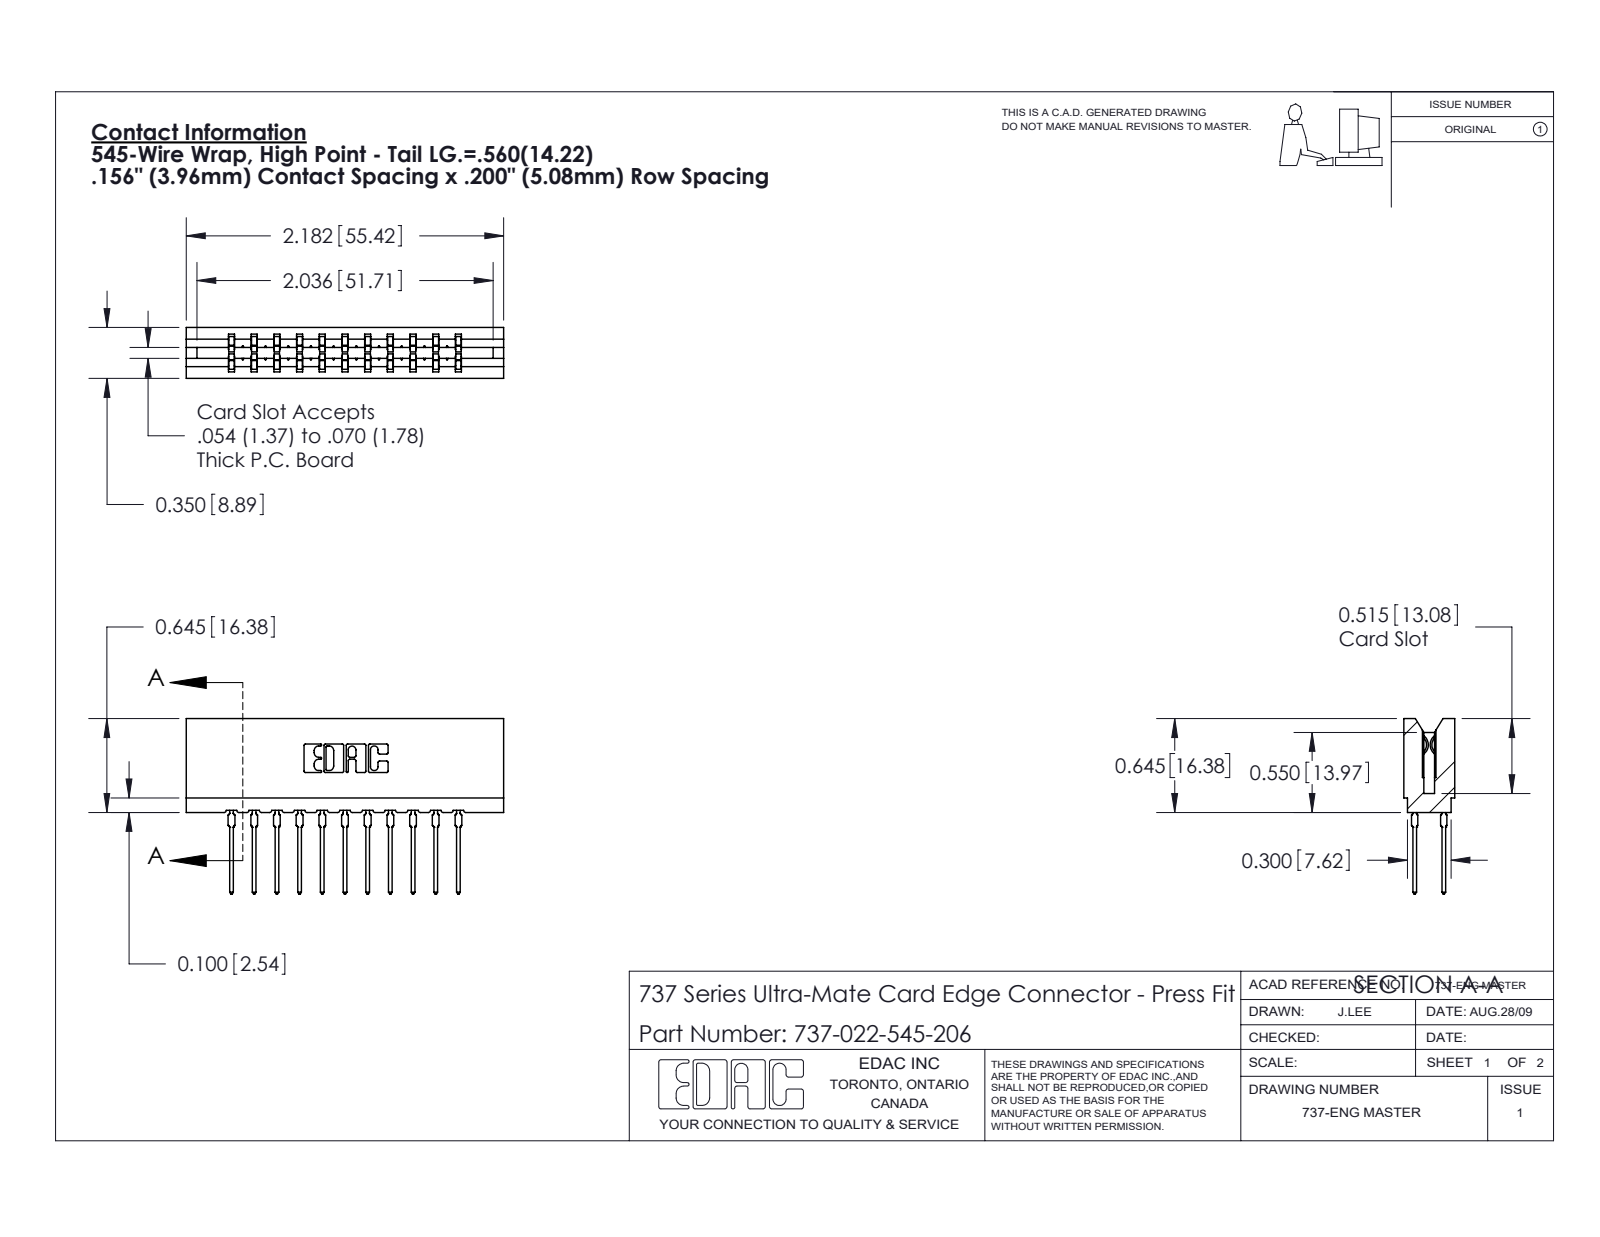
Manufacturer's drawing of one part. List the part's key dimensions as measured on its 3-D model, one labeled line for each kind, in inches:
Part name (STEP PRODUCT): 737-022-545-206; 745-292-001_545; 737 Part_Insulator Option - 06
STEP written by: SolidWorks 2020 (CONFIG_CONTROL_DESIGN)
Units: inches
Bodies: 23 solids, 2075 faces (1078 planar, 425 cylindrical, 572 other)
Overall size (bounding box): 2.182 × 1.206 × 0.35
Volume: 0.35 in³ · Surface area: 12.44 in²
Partial cylindrical surfaces — rounded edges, fillets, slot ends (radius × count): R0.021 ×44, R0.01 ×22, R0.015 ×22, R0.005 ×8, R0.011 ×8, R0.007 ×6, R0.031 ×6, R0.026 ×3
Main face-to-face distances: 0.156, 0.138, 0.212, 0.35, 0.624, 0.354, 0.312, 0.78, 0.468, 0.063
